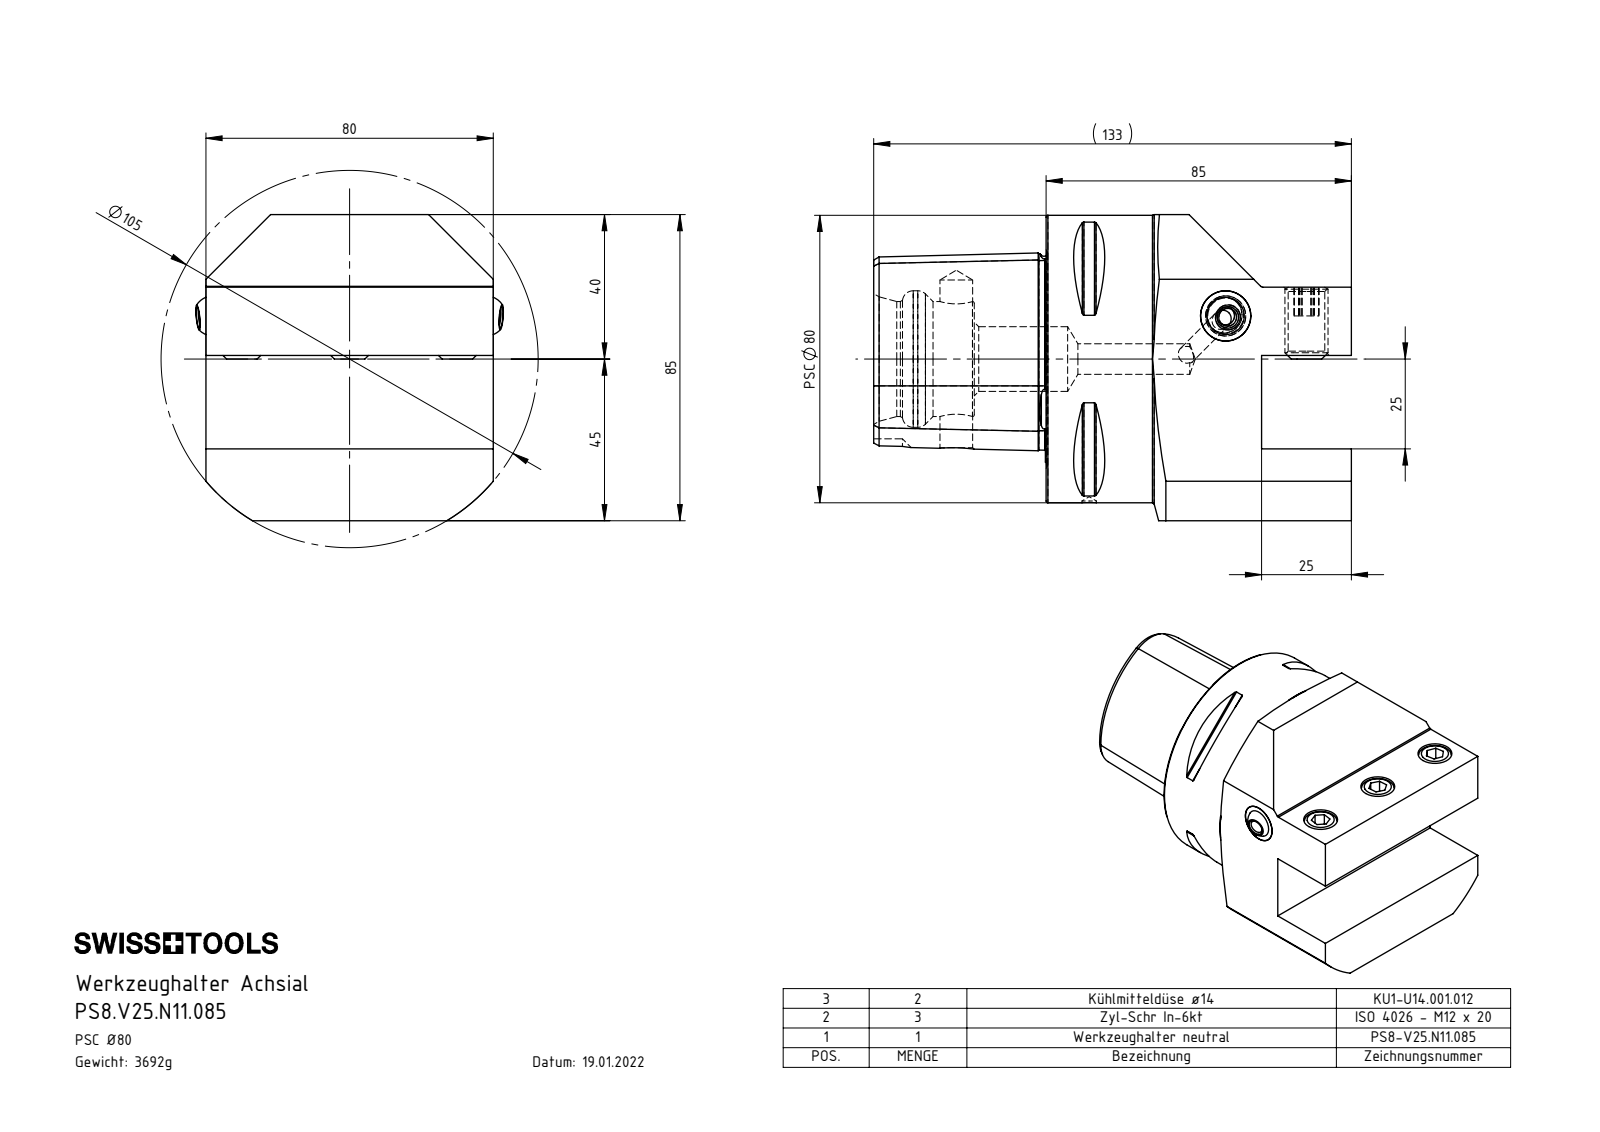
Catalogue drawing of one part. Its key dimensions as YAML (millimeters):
part_name: "KU1-U12.002.010_A; ISO 4026 - M12 x 20; PS8.V25.N11.085; KU1-U12.003.010_B (+3 more)"
step_written_by: "SolidWorks 2017 (AUTOMOTIVE_DESIGN)"
units: millimeters
bodies: {solids: 10, faces: 243, planar: 94, cylindrical: 45, other: 104}
overall_size: [133, 85.1, 81.16]
volume: 470932
surface_area: 58826
round_holes:
  - {diameter: 5, count: 3}
  - {diameter: 10.2, count: 3}
  - {diameter: 4, count: 1}
  - {diameter: 8.5, count: 1}
  - {diameter: 8.8, count: 1}
  - {diameter: 9.1, count: 1}
  - {diameter: 10, count: 1}
  - {diameter: 11, count: 1}
  - {diameter: 18, count: 1}
  - {diameter: 32, count: 1}
  - {diameter: 38, count: 1}
round_bosses_or_shafts:
  - {diameter: 12, count: 4}
  - {diameter: 80, count: 1}
partial_cylinders:
  - {radius: 0.5, count: 8}
  - {radius: 0.8, count: 1}
  - {radius: 6, count: 1}
  - {radius: 52.5, count: 1}
face_to_face_distances: [20, 25, 80.2, 60, 85, 45, 65, 46, 26, 19]
hole_center_spacings: [30, 67.53, 102.01, 37, 60, 60.5, 97.5]
